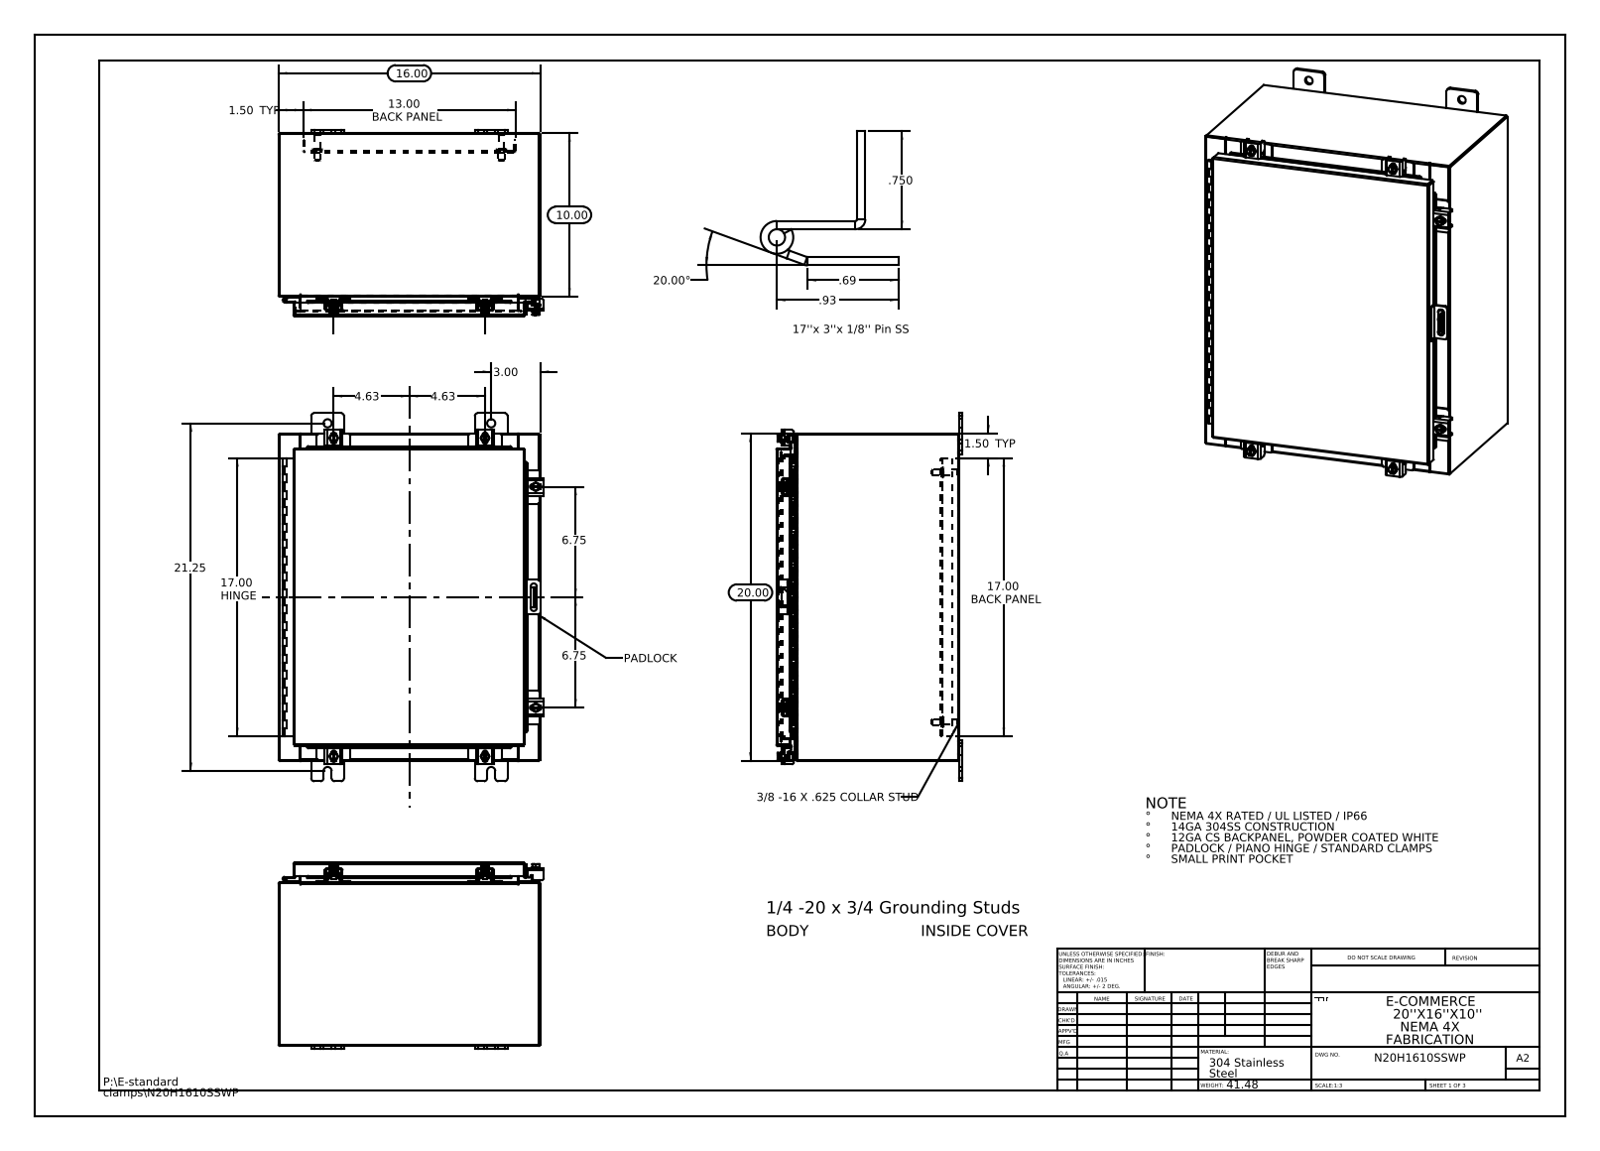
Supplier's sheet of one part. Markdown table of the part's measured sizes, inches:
| quantity | value |
| --- | --- |
| part name | N20H1610SSWP 125 Pin Hinge; N20H1610SSWP Hinge Enclosure Side2; N20H1610SSWP Mounting Feet; N20H1610SSWP 22101002 (+8 more) |
| STEP written by | SolidWorks 2013 (CONFIG_CONTROL_DESIGN) |
| units | inches |
| bodies | 47 solids, 1613 faces (860 planar, 657 cylindrical, 96 other) |
| overall size | 22.5 × 16.211 × 11.389 |
| volume | 146.2 in³ |
| surface area | 3 722 in² |
| round holes (diameter × count) | 0.5 × 8, 0.213 × 6, 0.26 × 6, 0.125 × 2, 0.125 × 1 |
| round bosses / shafts (diameter × count) | 0.25 × 7, 0.5 × 6, 0.399 × 6, 0.625 × 4, 0.375 × 4, 0.33 × 4 |
| partial cylindrical surfaces (radius × count) | 0.06 × 30, 0.013 × 25, 0.19 × 24, 0.088 × 21, 0.12 × 12, 0.141 × 12, 0.125 × 10, 0.05 × 9 |
| main face-to-face distances | 0.075, 11.126, 15.925, 19.925, 11.201, 11.051, 0.104, 1, 1.075, 10.051 |
| hole center spacings | 17.38, 1.858, 2.276, 2.326, 2.326, 3.065, 4.297, 9.25 |
